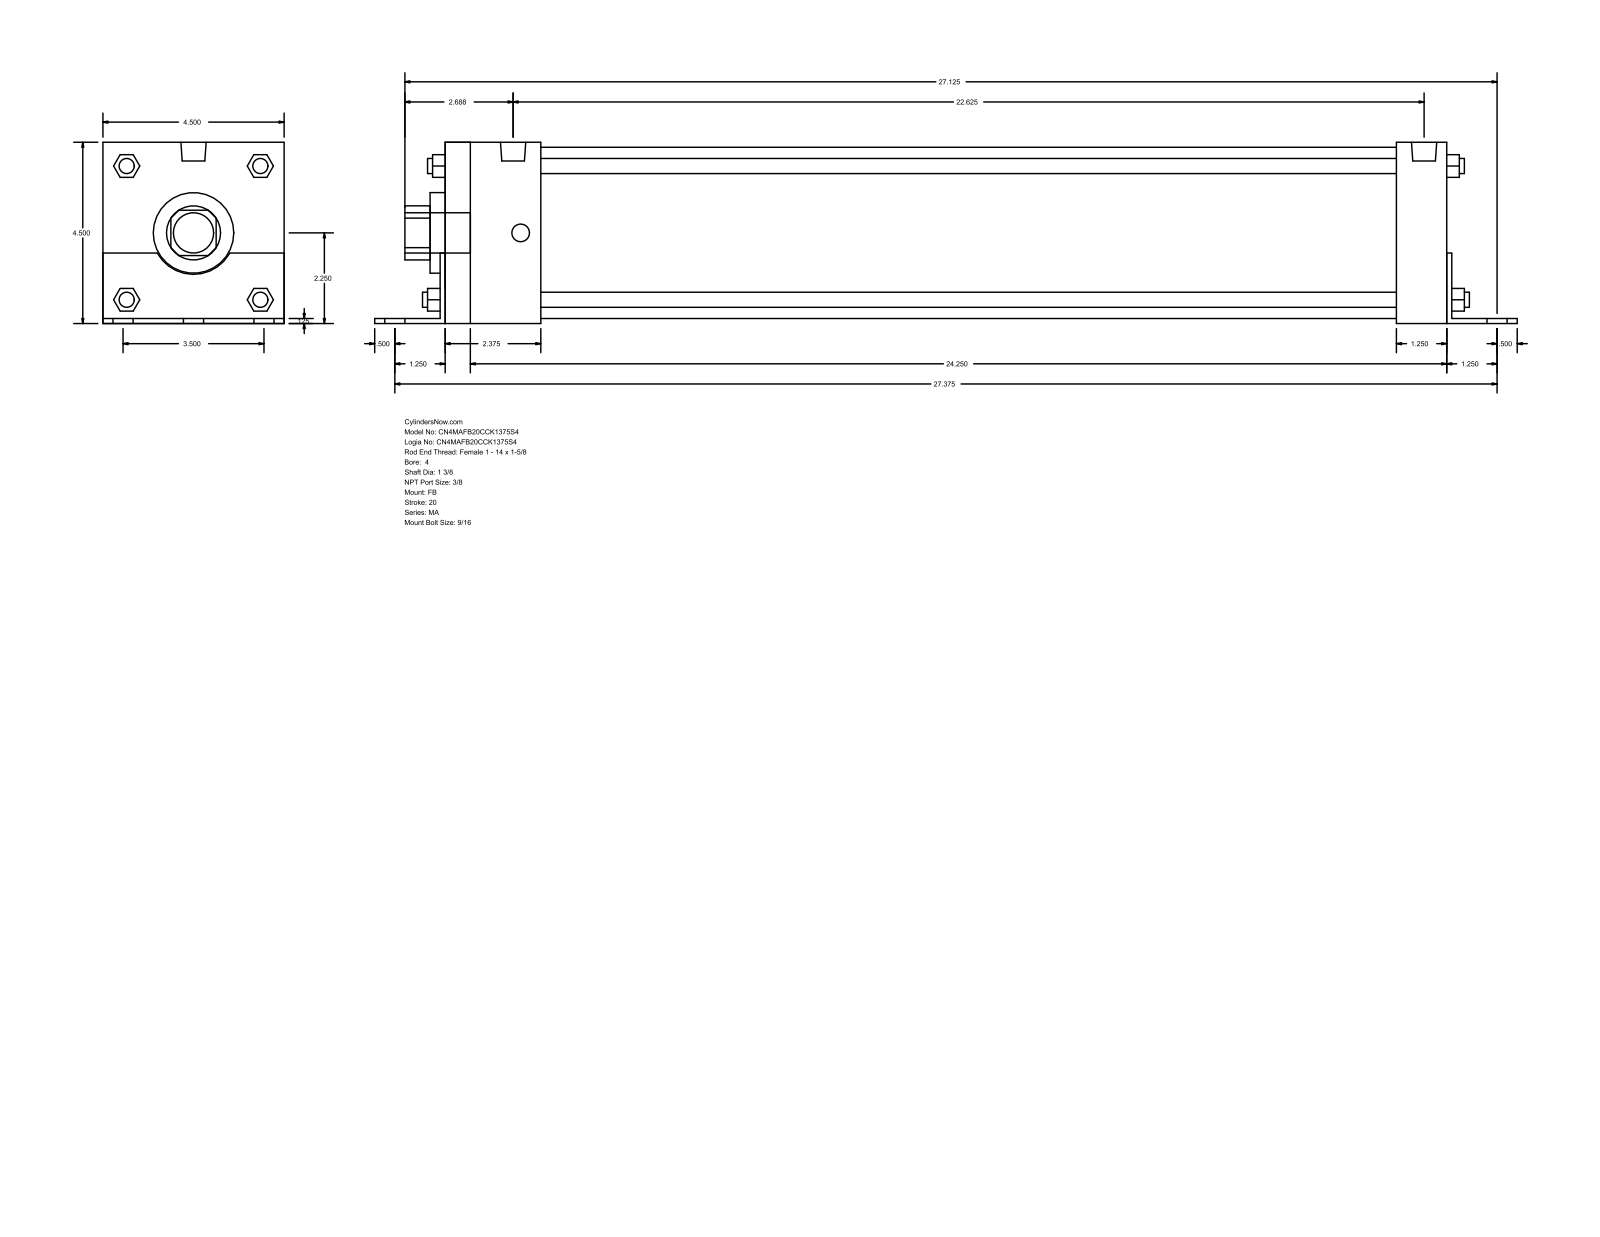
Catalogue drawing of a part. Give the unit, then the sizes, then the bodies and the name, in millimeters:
Units: millimetres
Overall size (bounding box): 720.73 × 114.35 × 114.3
Round holes (diameter × count): ⌀34.92 ×1, ⌀50.8 ×1, ⌀107.95 ×1
Round bosses / shafts (diameter × count): ⌀14.29 ×6, ⌀11.11 ×4, ⌀9.53 ×4, ⌀15.93 ×2, ⌀25.4 ×1
Partial cylindrical surfaces — rounded edges, fillets, slot ends (radius × count): R17.06 ×1, R26.16 ×1
Main face-to-face distances: 114.3, 3.17, 114.35, 3.12, 111.18, 635, 631.83, 60.32, 638.17, 31.75
Bodies: 0 solids, 140 faces (105 planar, 35 cylindrical, 0 other)
Part name (STEP PRODUCT): MA_FB__0400_1.375
STEP written by: GSSL Pune (CONFIG_CONTROL_DESIGN)
